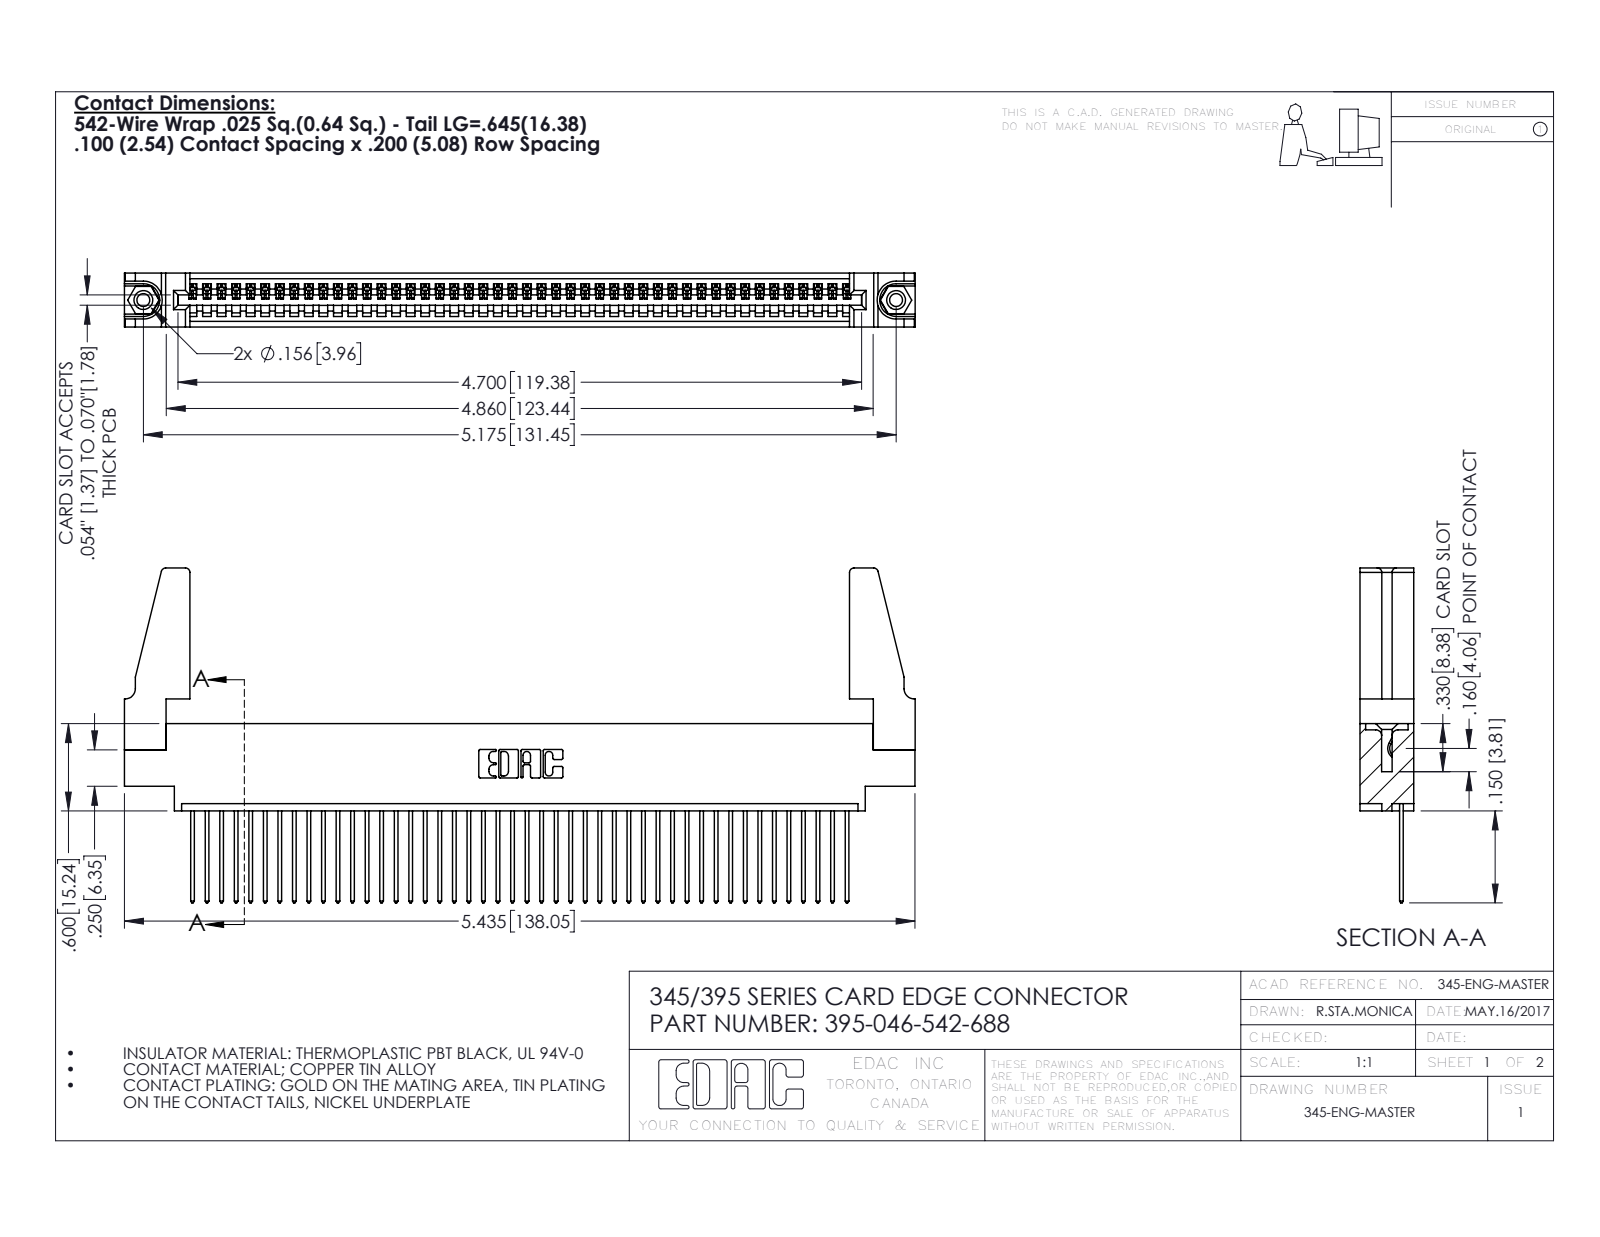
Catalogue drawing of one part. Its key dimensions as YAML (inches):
part_name: "345-250-001_345-250-001-102; 345 Part_0.170 Offset - 0.156 Dia-TH; 345-292-001_345-293-142; 345-220-078_345-220-088 (+1 more)"
step_written_by: "SolidWorks 2016 (CONFIG_CONTROL_DESIGN)"
units: inches
bodies: {solids: 51, faces: 2922, planar: 1996, cylindrical: 910, other: 16}
overall_size: [5.436, 2.302, 0.37]
volume: 1
surface_area: 33.19
round_holes:
  - {diameter: 0.089, count: 2}
  - {diameter: 0.125, count: 2}
  - {diameter: 0.156, count: 2}
  - {diameter: 0.064, count: 1}
round_bosses_or_shafts:
  - {diameter: 0.155, count: 2}
partial_cylinders:
  - {radius: 0.006, count: 92}
  - {radius: 0.01, count: 92}
  - {radius: 0.01, count: 22}
  - {radius: 0.03, count: 8}
  - {radius: 0.007, count: 6}
  - {radius: 0.031, count: 6}
  - {radius: 0.026, count: 3}
  - {radius: 0.031, count: 2}
face_to_face_distances: [0.072, 0.298, 0.37, 0.098, 0.272, 0.025, 0.2, 0.225, 0.175, 0.149]
hole_center_spacings: [0.27, 4.939, 5.175]
